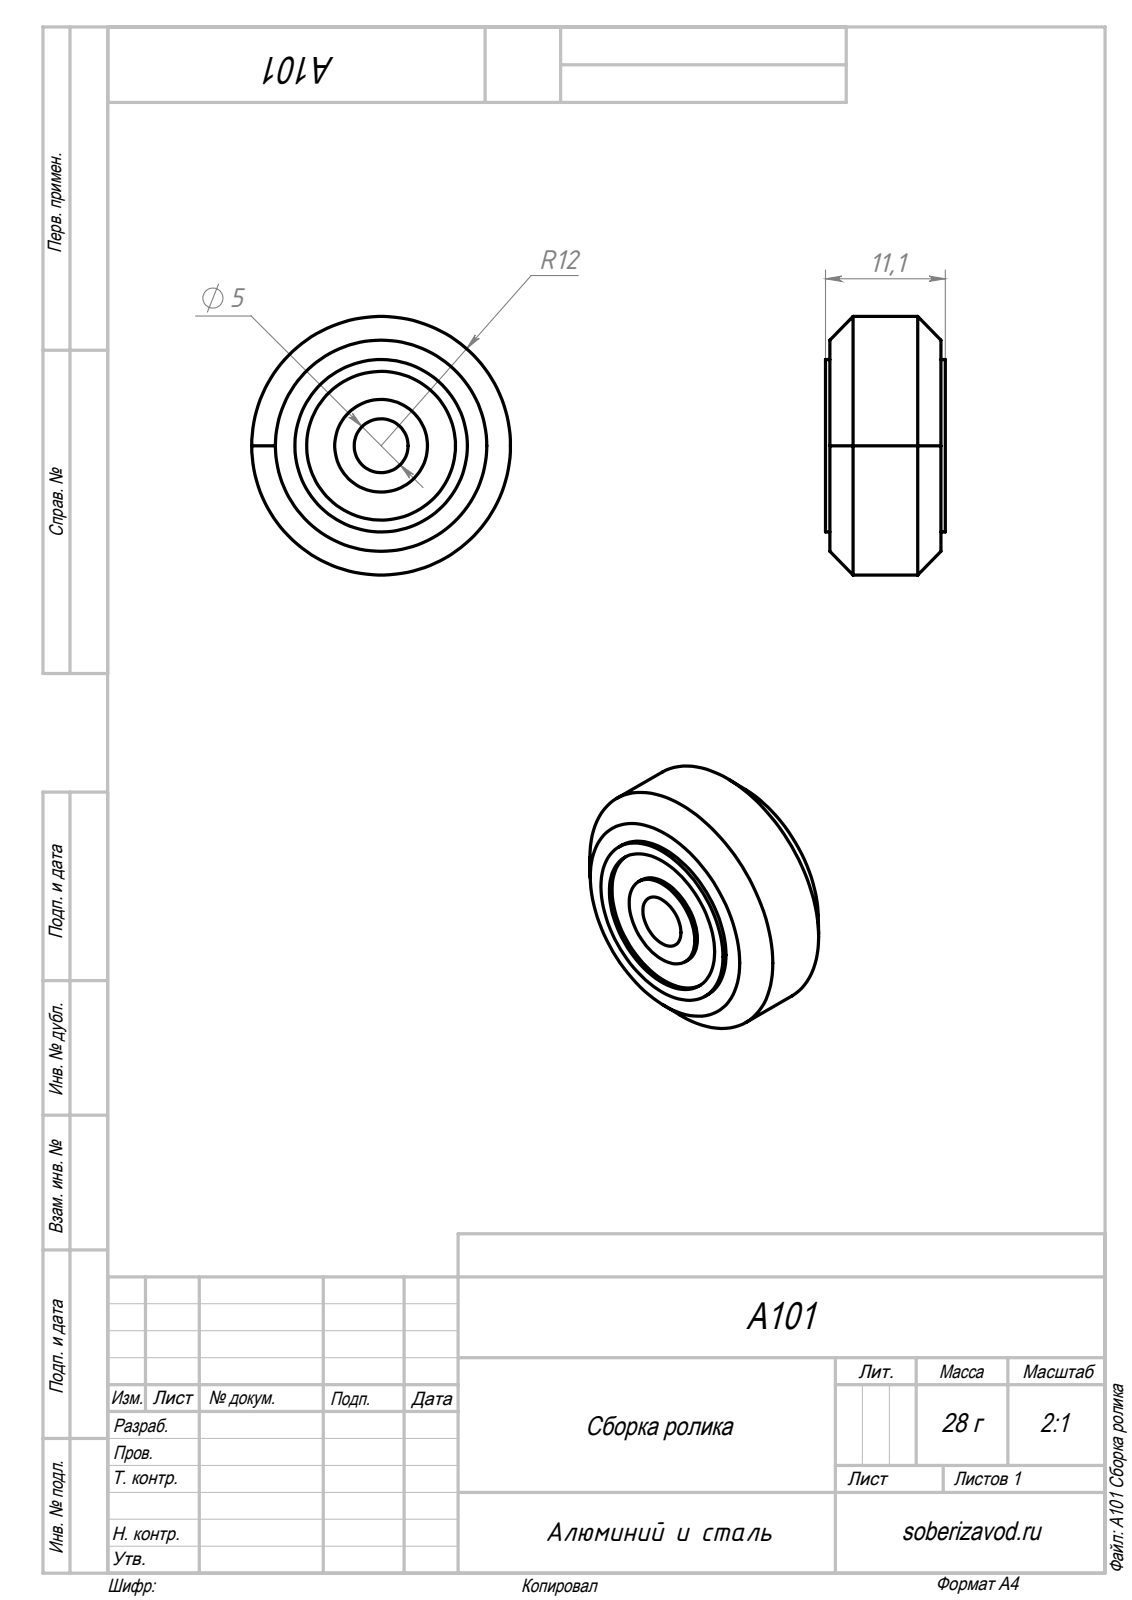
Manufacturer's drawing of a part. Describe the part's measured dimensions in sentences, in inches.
The part is named "A211 Высокоточная дистанционная шайба 5 мм_00; A101 Сборка ролика; A180 Подшипник 625rs, O 5 O 16". Its 3-D file was written by "SolidWorks 2018 (AUTOMOTIVE_DESIGN)". It is 4 solids with 58 faces: 18 planar, 36 cylindrical and 4 other. Overall it measures 0.945 by 0.945 by 0.437 inches. Its volume is 0.247 cubic inches and its surface area 5.155 square inches. Round holes: 1 of diameter 0.197, 1 of diameter 0.205, 1 of diameter 0.543, 1 of diameter 0.551, 1 of diameter 0.63. Round bosses or shafts: 1 of diameter 0.945, 1 of diameter 0.394, 1 of diameter 0.339. The main face-to-face distances are 0.183, 0.014, 0.24, 0.224, 0.238, 0.016, 0.181, 0.169, 0.226, 0.407.
